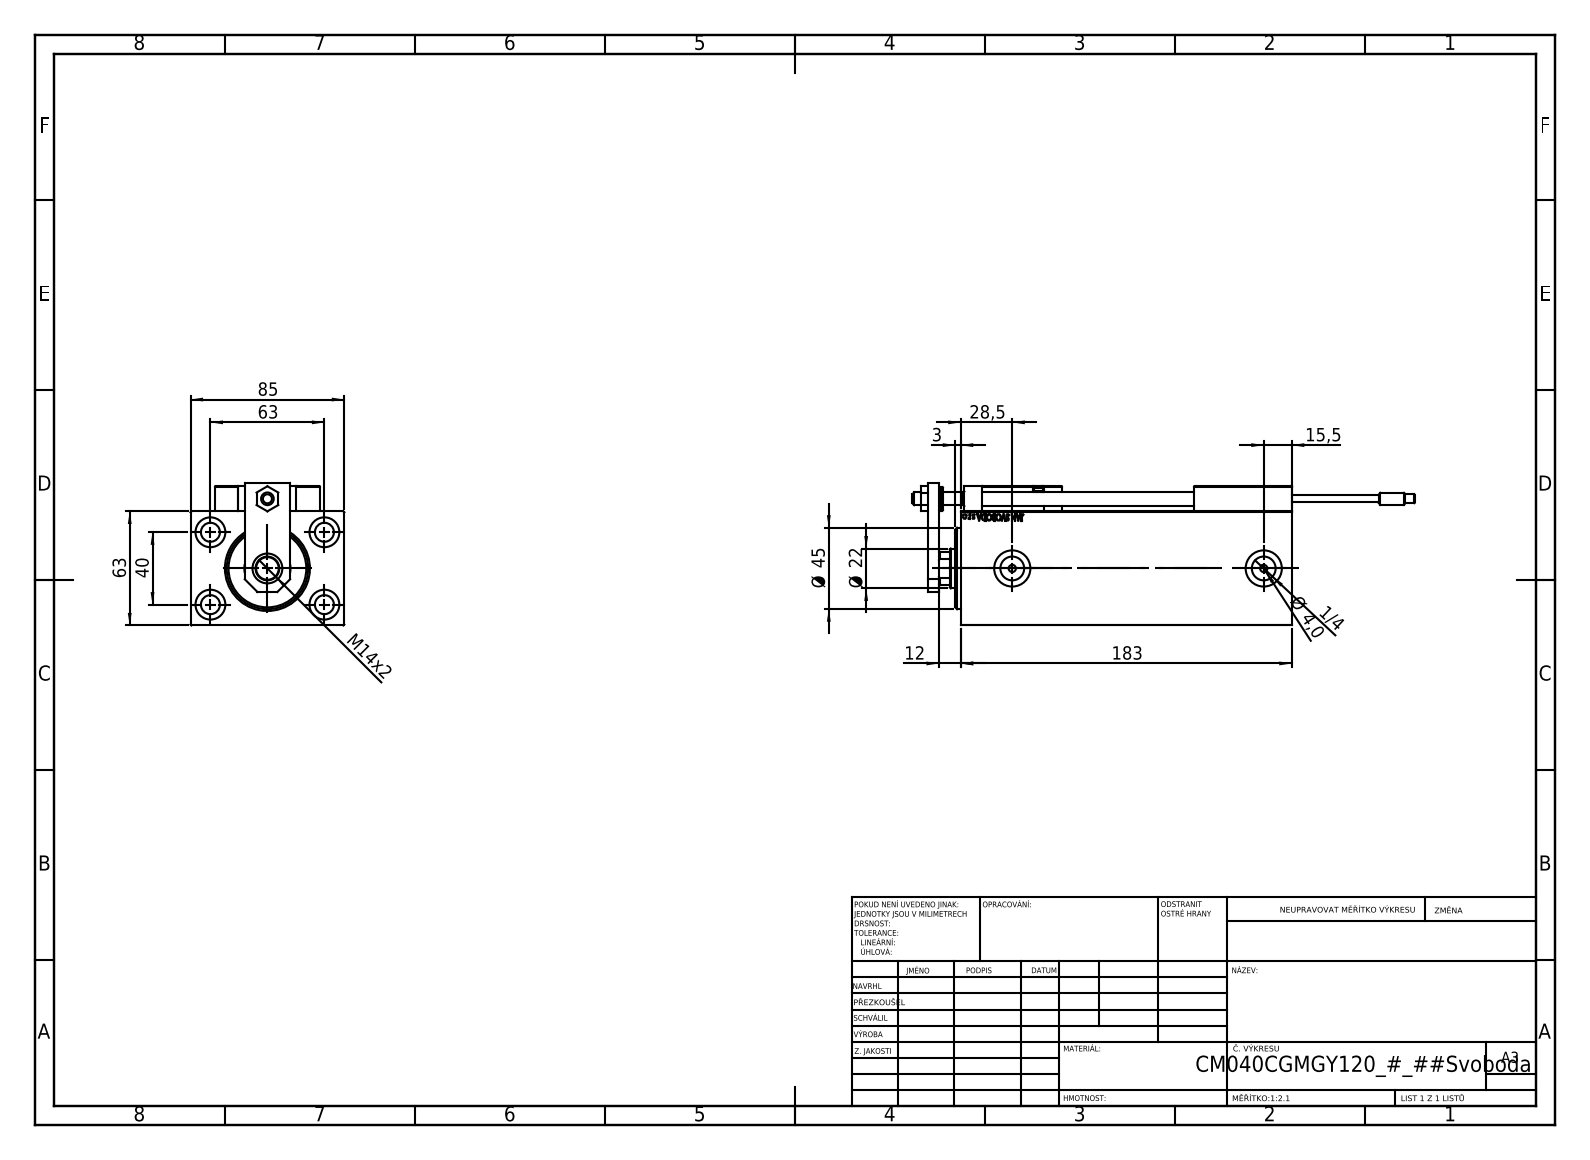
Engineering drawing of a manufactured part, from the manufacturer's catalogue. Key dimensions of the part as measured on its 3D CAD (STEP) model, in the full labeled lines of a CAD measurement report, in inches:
Part name (STEP PRODUCT): SWITCH DIM B,W; V450CM_C_Body; SWITCH X; MAGNET (+7 more)
STEP written by: SolidWorks 2019 (CONFIG_CONTROL_DESIGN)
Units: inches
Bodies: 23 solids, 1304 faces (562 planar, 196 cylindrical, 546 other)
Overall size (bounding box): 10.933 × 3.346 × 3.091
Volume: 52.22 in³ · Surface area: 254.4 in²
Round holes (diameter × count): ⌀0.157 ×6, ⌀0.315 ×5, ⌀0.65 ×5, ⌀0.126 ×4, ⌀0.413 ×4, ⌀0.197 ×2, ⌀0.518 ×2, ⌀0.787 ×2, ⌀0.276 ×1, ⌀0.492 ×1, ⌀0.866 ×1, ⌀1.004 ×1
Round bosses / shafts (diameter × count): ⌀0.197 ×4, ⌀0.256 ×2, ⌀0.15 ×2, ⌀0.512 ×1, ⌀0.433 ×1
Partial cylindrical surfaces — rounded edges, fillets, slot ends (radius × count): R0.012 ×30, R0.118 ×2, R0.413 ×1
Main face-to-face distances: 2.48, 3.346, 0.472, 6.732, 7.205, 0.551, 3.031, 0.591, 0.709, 1.181
Hole centre spacings: 1.469, 0.448, 0.787, 1.165, 1.169, 1.42, 1.438, 1.575
